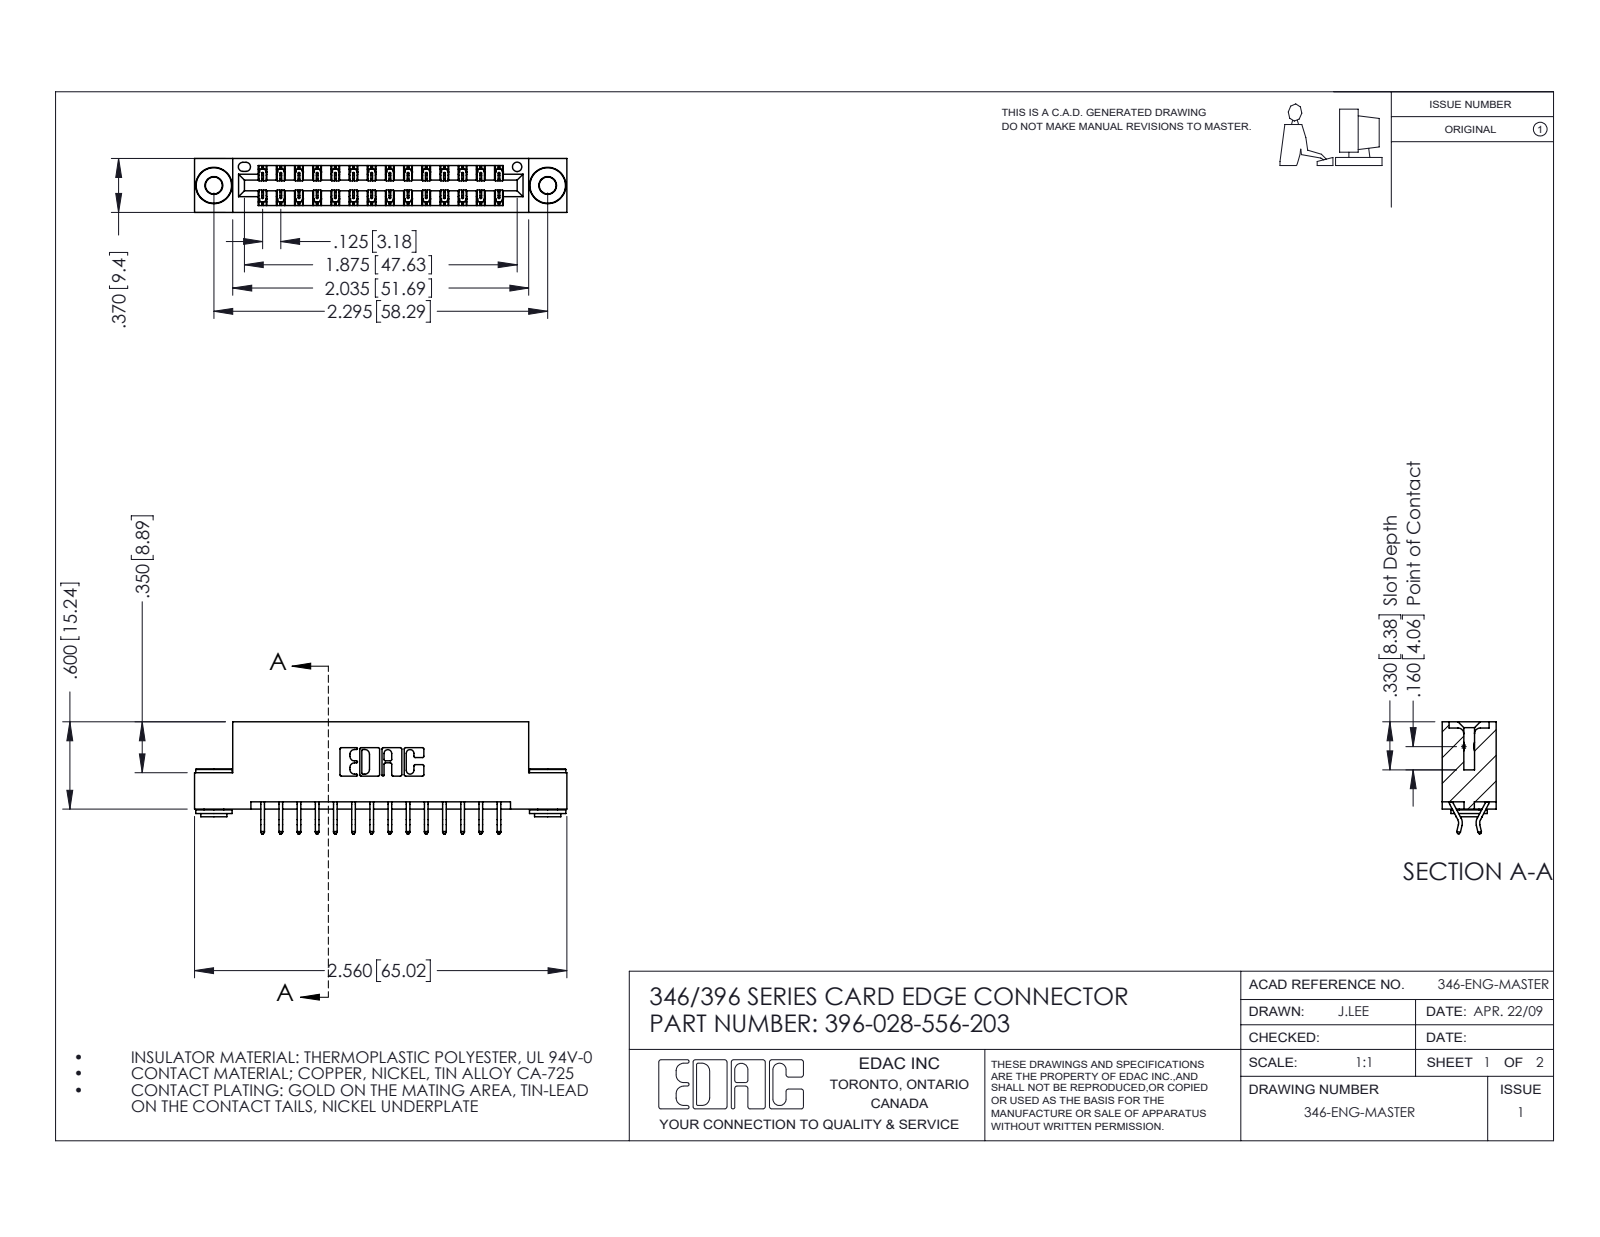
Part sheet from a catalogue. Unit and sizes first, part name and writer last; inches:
Units: inches
Overall size (bounding box): 2.56 × 0.77 × 0.37
Round holes (diameter × count): ⌀0.116 ×2, ⌀0.156 ×2, ⌀0.064 ×1
Round bosses / shafts (diameter × count): ⌀0.25 ×2, ⌀0.18 ×2, ⌀0.136 ×2
Partial cylindrical surfaces — rounded edges, fillets, slot ends (radius × count): R0.006 ×42, R0.01 ×22, R0.007 ×6, R0.031 ×6, R0.026 ×3, R0.01 ×2, R0.014 ×2, R0.022 ×2
Main face-to-face distances: 0.25, 0.048, 0.322, 0.37, 0.025, 0.072, 0.298, 0.275, 0.148, 0.222
Hole centre spacings: 0.246, 2.089, 2.295
Volume: 0.375 in³ · Surface area: 12.69 in²
Bodies: 31 solids, 1784 faces (1178 planar, 598 cylindrical, 8 other)
Part name (STEP PRODUCT): 345-250-002_345-250-002-102; 396-028-556-203; 345-292-001_556 Tail; 346 Part_Flush Mounting Lugs - 0.156 Dia-TH
STEP written by: SolidWorks 2016 (CONFIG_CONTROL_DESIGN)
